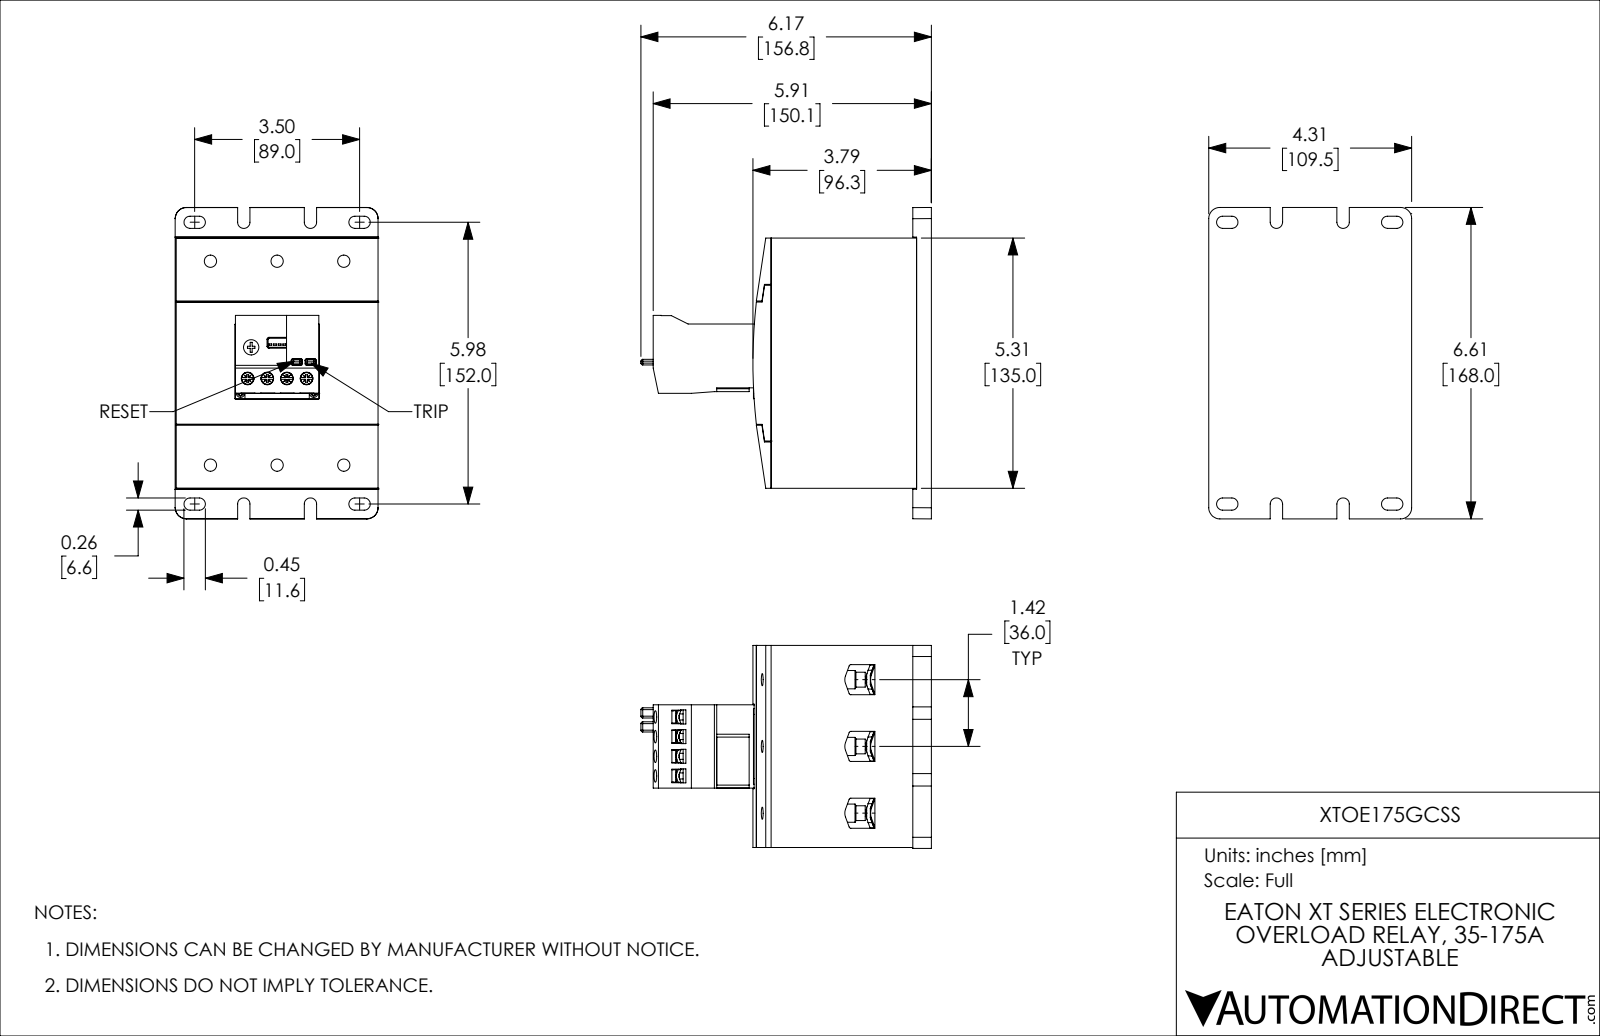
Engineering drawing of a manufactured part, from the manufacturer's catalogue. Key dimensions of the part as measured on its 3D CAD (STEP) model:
Part name (STEP PRODUCT): XTOE175GCSS
STEP written by: SolidWorks 2018 (AUTOMOTIVE_DESIGN)
Units: inches
Bodies: 31 solids, 1770 faces (908 planar, 492 cylindrical, 370 other)
Overall size (bounding box): 6.614 × 6.171 × 4.311
Volume: 88.82 in³ · Surface area: 297.2 in²
Round holes (diameter × count): ⌀0.098 ×6, ⌀0.26 ×6, ⌀0.39 ×6, ⌀0.11 ×4, ⌀0.14 ×4, ⌀0.236 ×4, ⌀0.268 ×4, ⌀0.086 ×2, ⌀0.126 ×2
Round bosses / shafts (diameter × count): ⌀0.387 ×6, ⌀0.315 ×6, ⌀0.236 ×6, ⌀0.138 ×6, ⌀0.134 ×4, ⌀0.128 ×4, ⌀0.11 ×4, ⌀0.098 ×4
Partial cylindrical surfaces — rounded edges, fillets, slot ends (radius × count): R0.008 ×48, R0.02 ×27, R0.006 ×24, R0.039 ×14, R0.055 ×12, R0.071 ×12, R0.095 ×12, R0.079 ×8
Main face-to-face distances: 3.091, 0.315, 3.406, 4.291, 3.405, 3.09, 5.315, 0.079, 1.26, 3.031
Hole centre spacings: 0.417, 0.835, 0.882, 1.417, 1.852, 1.944, 2.085, 2.499
